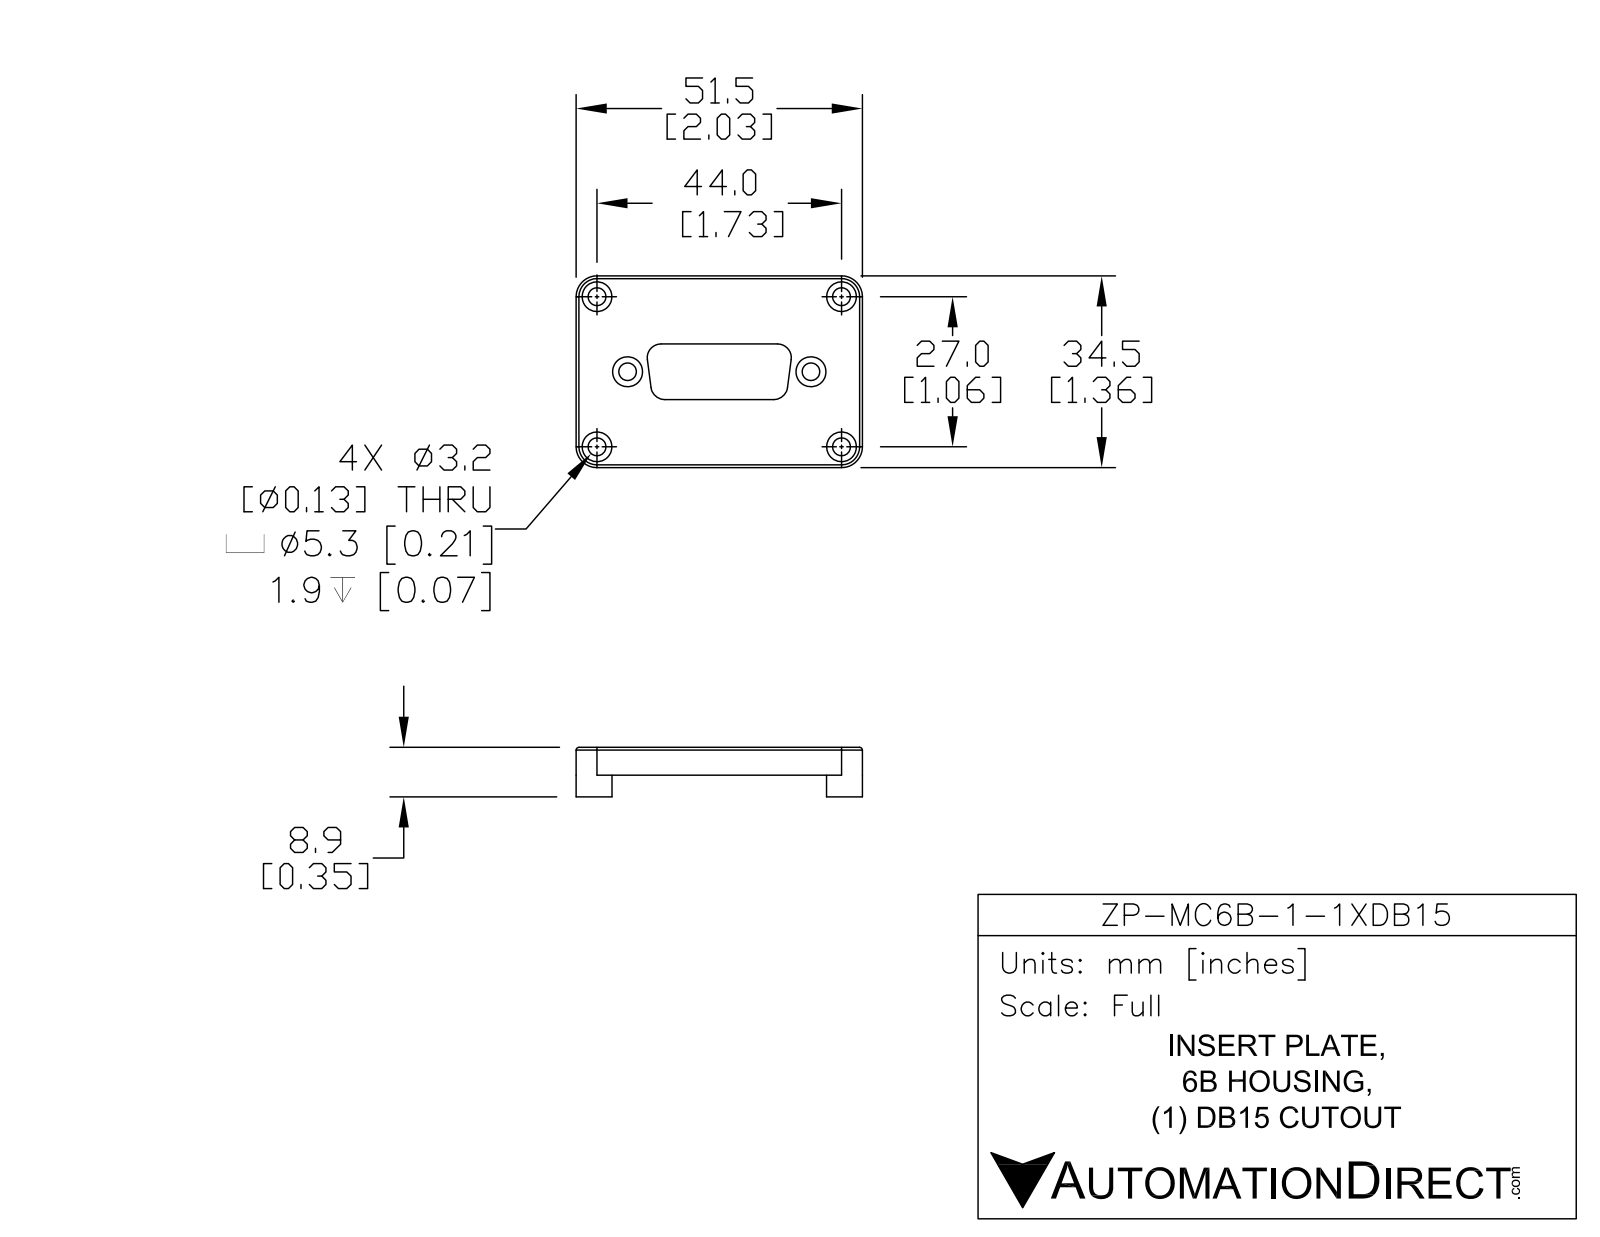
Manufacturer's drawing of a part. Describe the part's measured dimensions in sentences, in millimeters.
The part is named "ZP-MC6B-2-1XDB15". Its 3-D file was written by "SolidWorks 2014 (AUTOMOTIVE_DESIGN)". It is 1 solid with 85 faces: 39 planar, 38 cylindrical and 8 other. Overall it measures 51.5 by 34.5 by 8.91 millimeters. Its volume is 4 859 cubic millimeters and its surface area 5 091 square millimeters. Round holes: 4 of diameter 3.21, 4 of diameter 5.35, 2 of diameter 3.15. Partial cylindrical surfaces (rounded edges, fillets, slot ends): 4 of radius 0.5, 4 of radius 2.5, 4 of radius 3.75. The main face-to-face distances are 2.4, 2.6, 5, 2.15, 2.85, 32.1, 34.5, 6.45, 45.05, 51.5. The hole center spacings are 14.58, 40.8, 27, 44, 51.62, 33.
